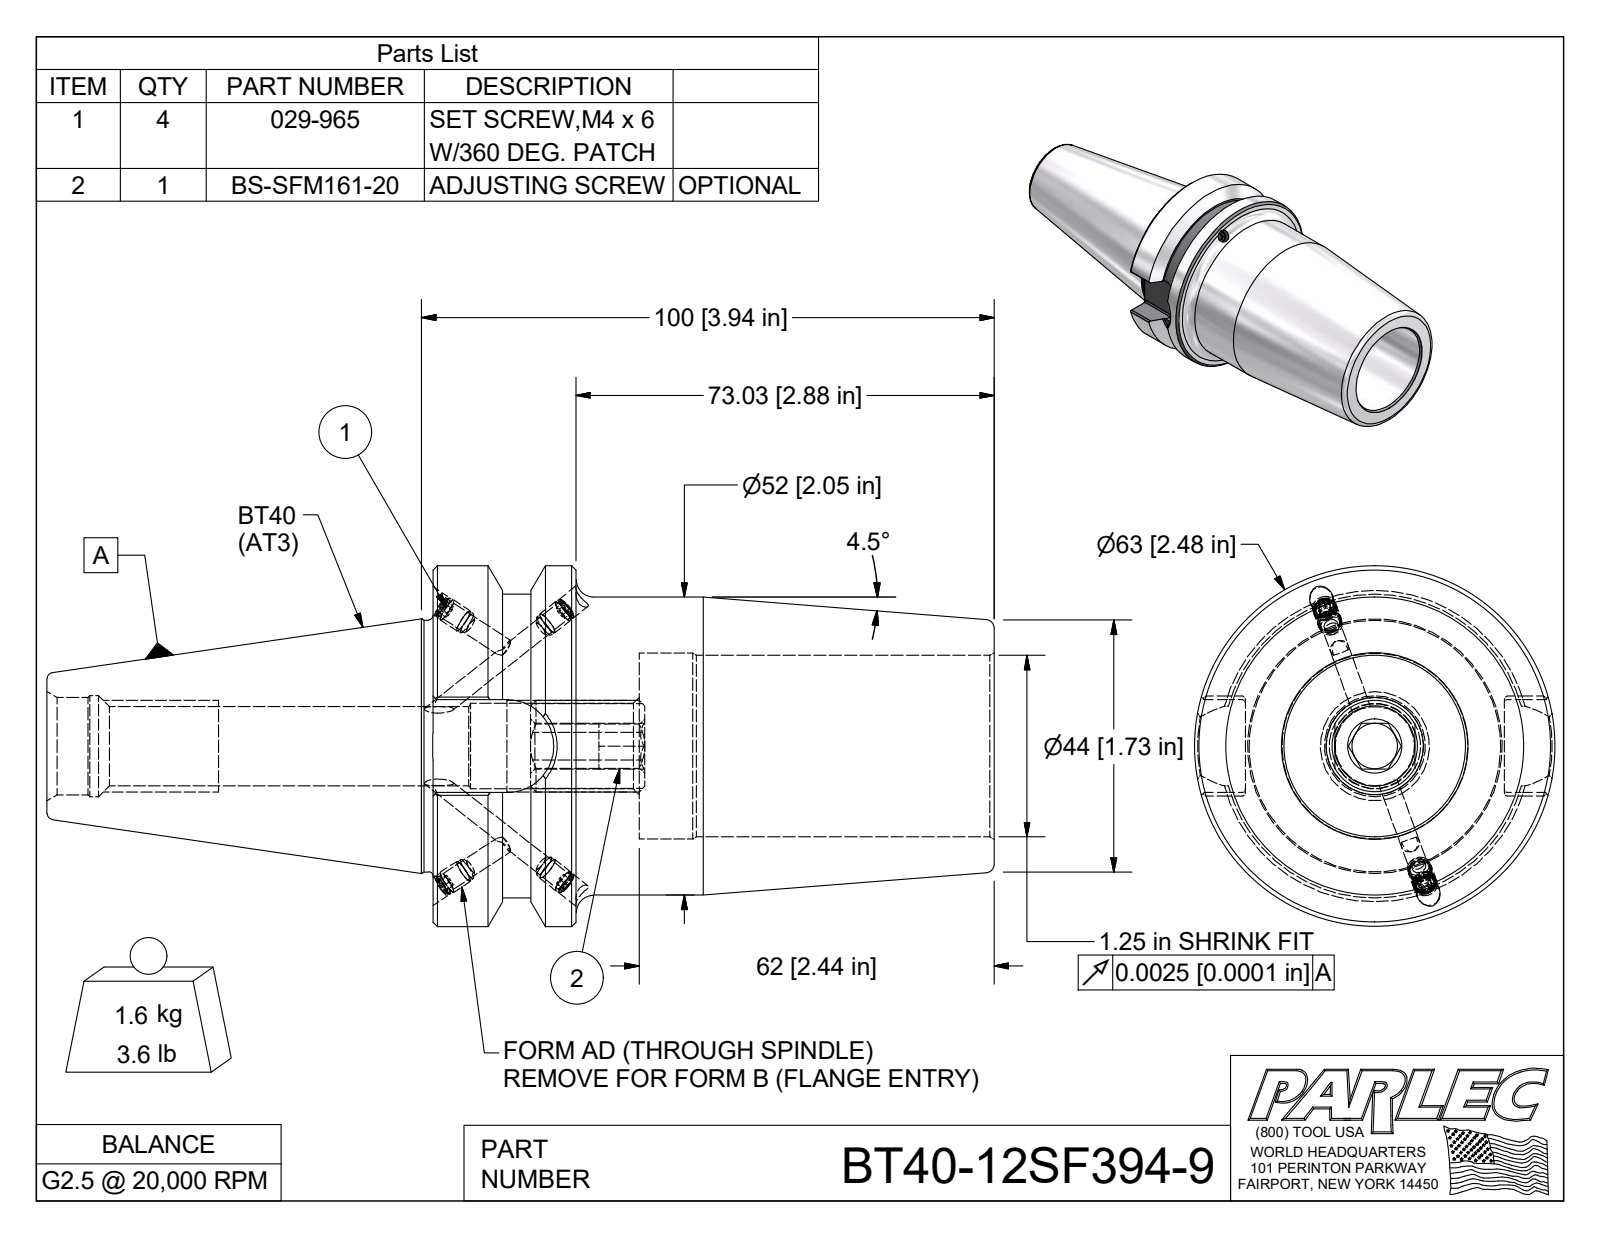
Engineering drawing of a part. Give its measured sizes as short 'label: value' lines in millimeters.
name: BT40-12SF394-9; BT40BC-12SF394-9-1; 029-965; BS-SFM161-20
written by: Autodesk Inventor 2009 (AUTOMOTIVE_DESIGN)
unit: mm
bodies: 6 solids, 173 faces (79 planar, 43 cylindrical, 51 other)
size: 165.4 × 63 × 63
volume: 209 400 mm³; area: 42 560 mm²
holes: 4× ⌀3.3, 4× ⌀4.1, 1× ⌀17.6, 1× ⌀31.7, 1× ⌀32.5
bosses: 4× ⌀4.2, 4× ⌀4, 1× ⌀63, 1× ⌀53, 1× ⌀52, 1× ⌀44.5, 1× ⌀43.9
rounds: 8× R0.5, 1× R8, 1× R8.1
face distances: 36, 98, 62, 25, 11, 73, 15.6, 29.6, 45.2, 67.4
